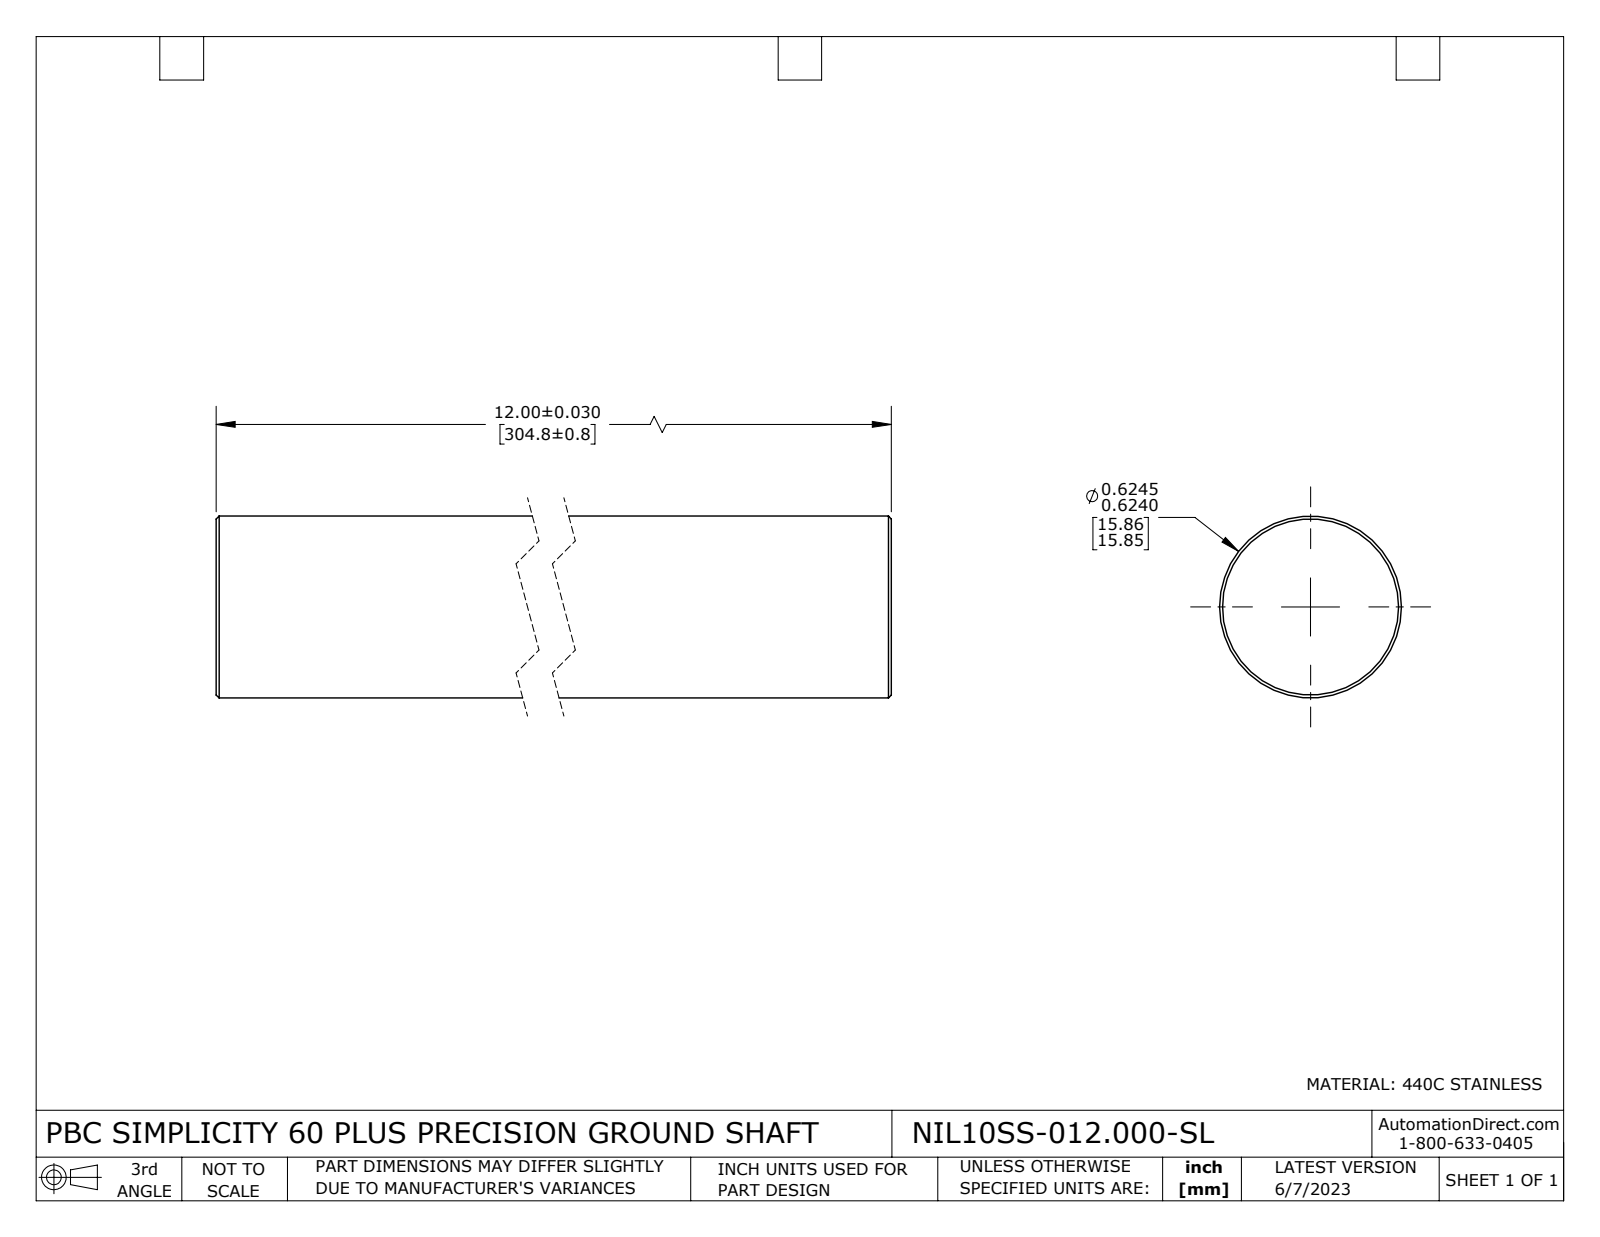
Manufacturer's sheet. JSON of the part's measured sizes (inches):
{"part_name": "NIL10SS-012.000-SL", "step_written_by": "SolidWorks 2021 (CONFIG_CONTROL_DESIGN)", "units": "inches", "bodies": {"solids": 1, "faces": 8, "planar": 2, "cylindrical": 2, "other": 4}, "overall_size": [12, 0.625, 0.625], "volume_in3": 3.681, "surface_area_in2": 24.15, "round_bosses_or_shafts": [[0.625, 1]], "face_to_face_distances": [12]}
